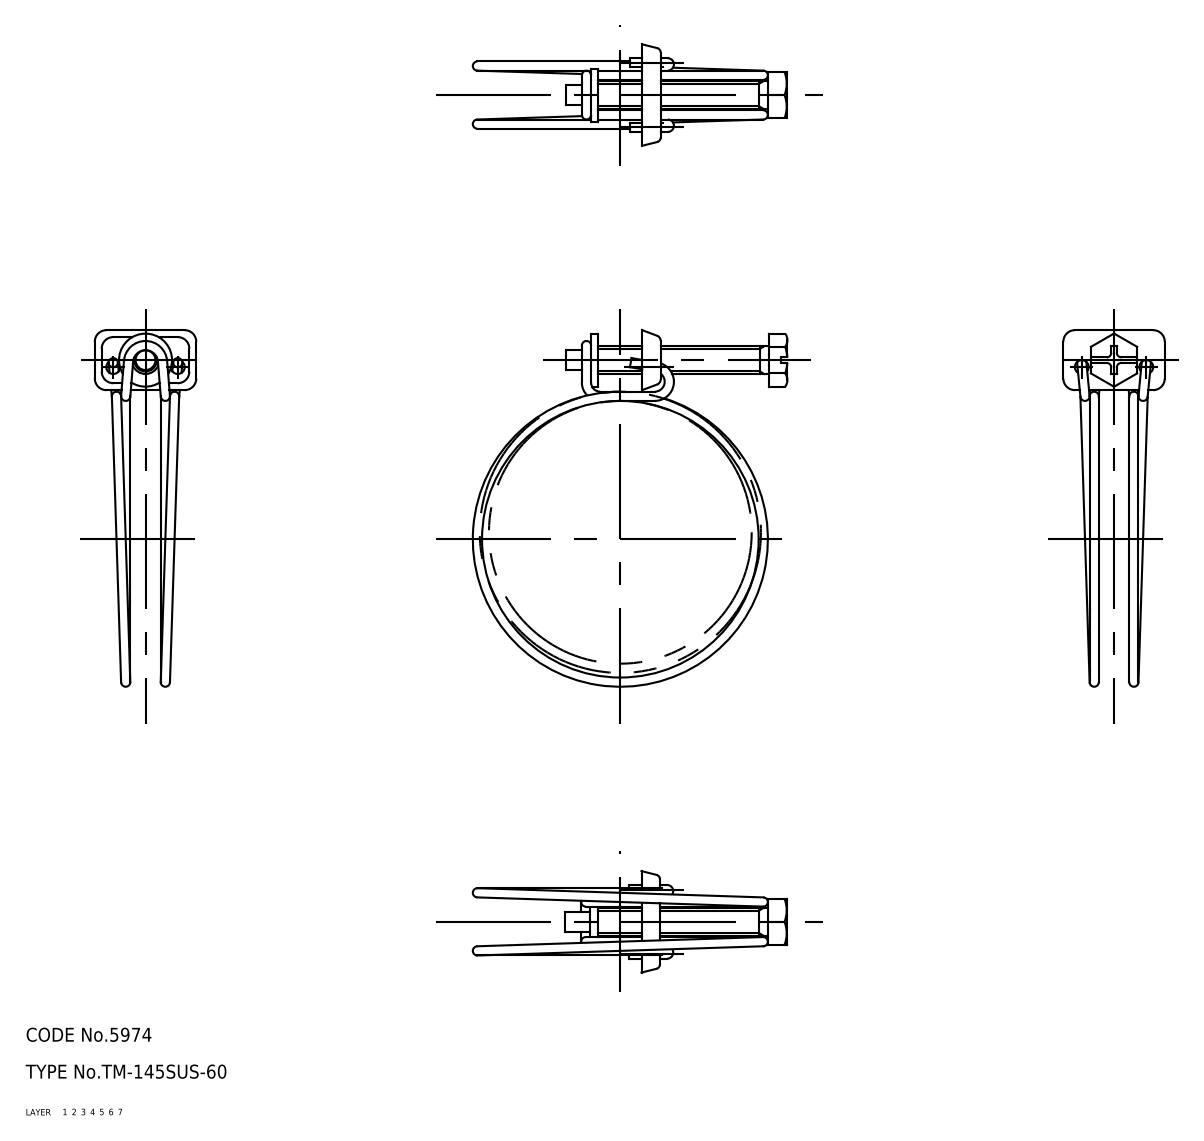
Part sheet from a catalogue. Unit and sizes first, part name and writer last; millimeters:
Units: millimetres
Overall size (bounding box): 77.35 × 68.25 × 22
Volume: 3 592 mm³ · Surface area: 5 118 mm²
Bodies: 3 solids, 119 faces (0 planar, 0 cylindrical, 119 other)
Part name (STEP PRODUCT): screw; holder; band; TM_145SUS_60_22454_36
STEP written by: CADfix (AUTOMOTIVE_DESIGN)
